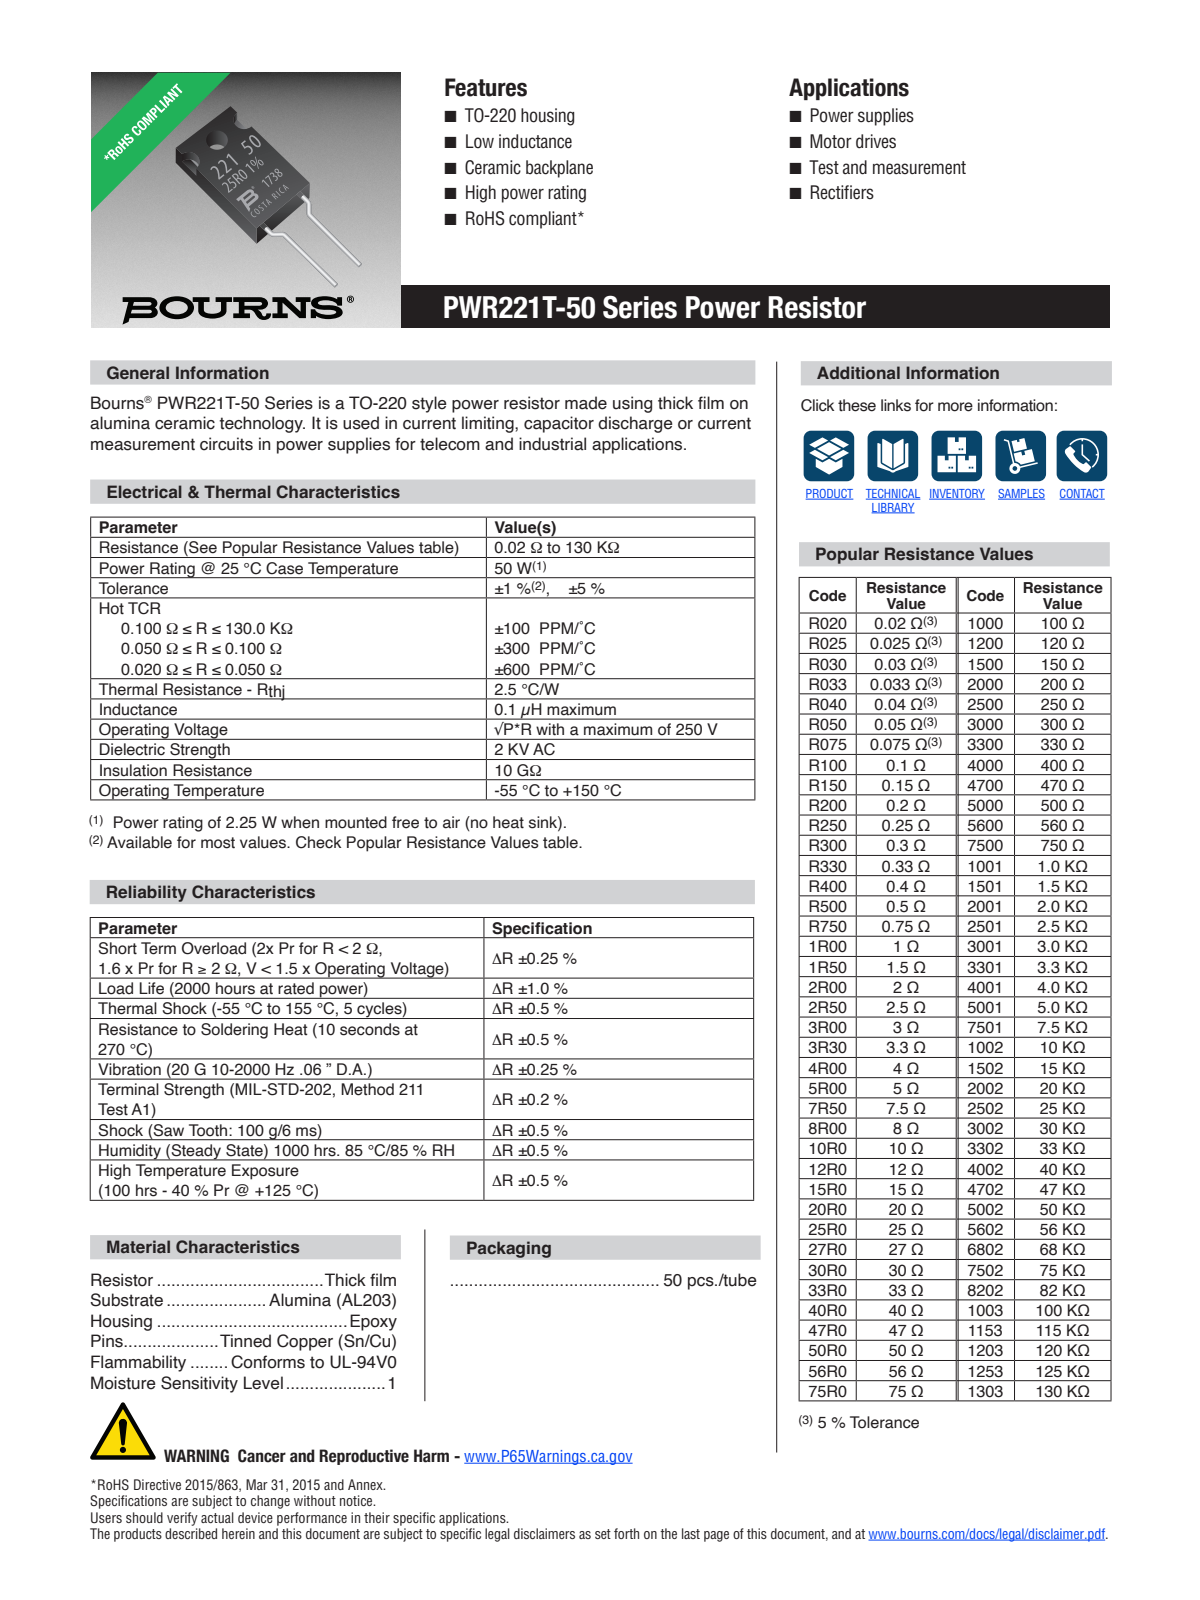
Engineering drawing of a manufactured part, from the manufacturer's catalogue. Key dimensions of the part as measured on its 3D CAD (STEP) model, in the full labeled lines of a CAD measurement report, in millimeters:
Part name (STEP PRODUCT): CERAMICA_POWER_RESISTOR_221; PIN_FORMADO_PWR-221; PIN_FORMADO_IZQPWR-221; HOUISNG_PWR_221 (+4 more)
STEP written by: CREO PARAMETRIC BY PTC INC, 2018050 (CONFIG_CONTROL_DESIGN)
Units: millimetres
Bodies: 33 solids, 693 faces (439 planar, 28 cylindrical, 226 other)
Overall size (bounding box): 29 × 10.4 × 3.2
Volume: 520 mm³ · Surface area: 912 mm²
Round holes (diameter × count): ⌀0.8 ×1, ⌀3.2 ×1
Round bosses / shafts (diameter × count): ⌀0.7 ×4, ⌀0.9 ×1
Partial cylindrical surfaces — rounded edges, fillets, slot ends (radius × count): R0.2 ×4, R0.3 ×4, R1.6 ×2, R0.2 ×1, R0.2 ×1, R0.6 ×1, R0.6 ×1
Main face-to-face distances: 3.2, 0.8, 2.3, 2.2, 1, 1, 10.4, 2.2, 1, 9.4
Hole centre spacings: 7.8
